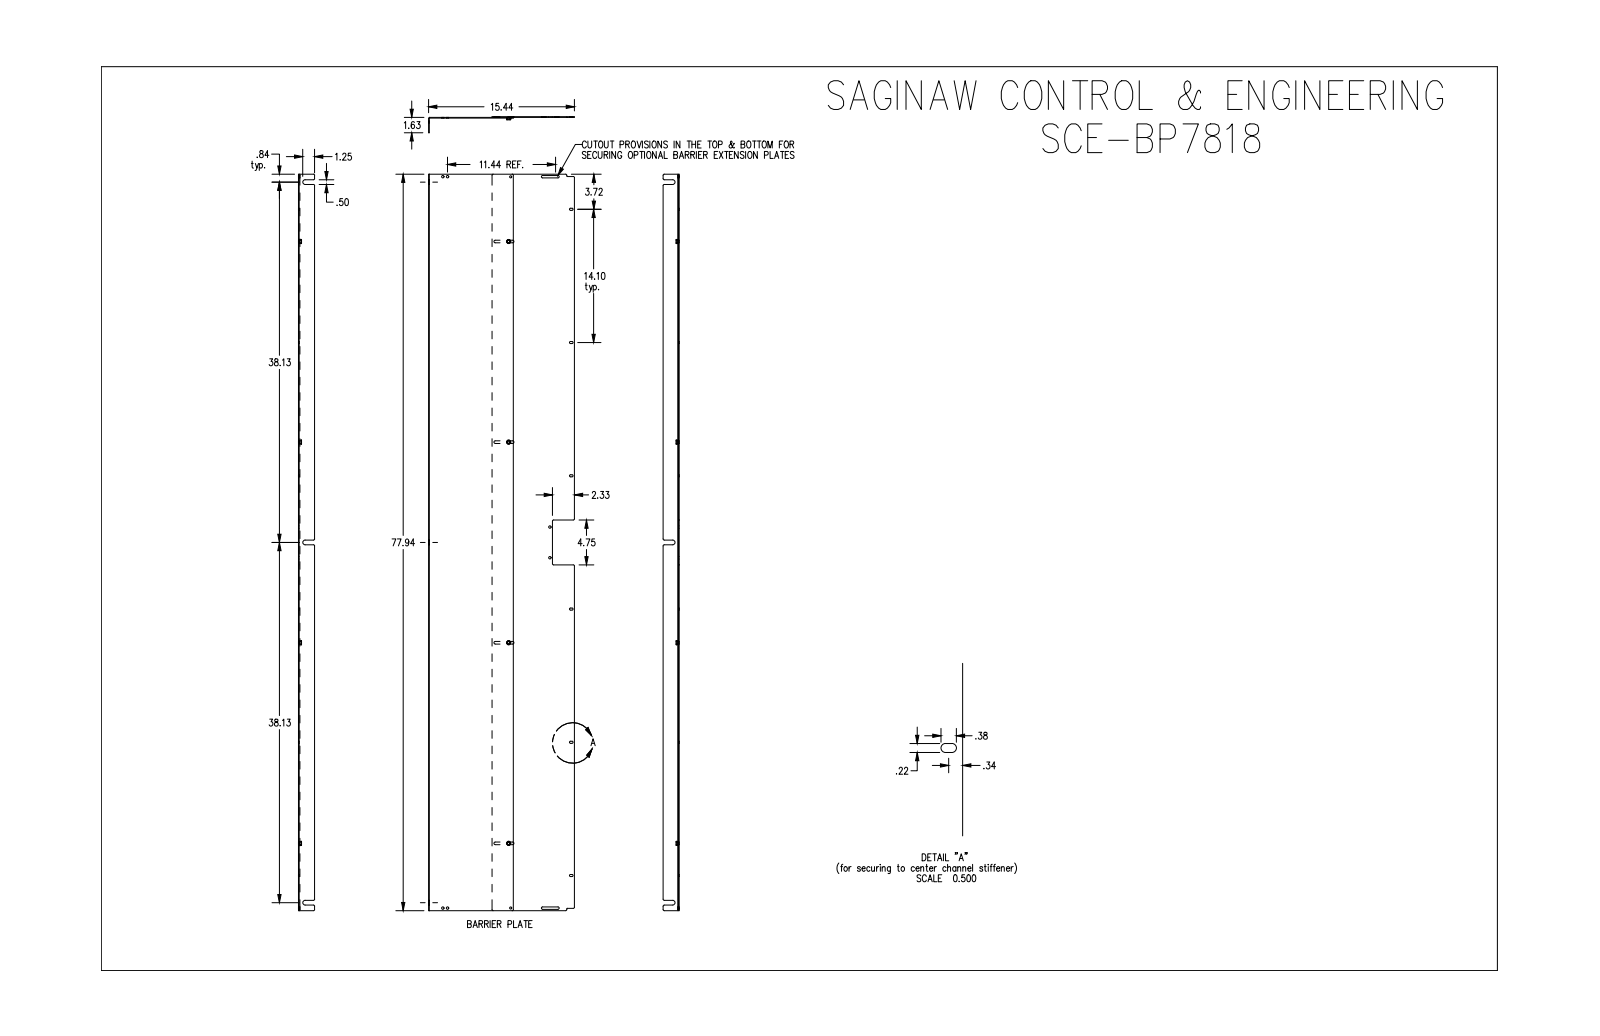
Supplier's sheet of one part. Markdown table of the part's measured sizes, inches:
| quantity | value |
| --- | --- |
| part name | SCE-BP7818 |
| STEP written by | SolidWorks 2019 (CONFIG_CONTROL_DESIGN) |
| units | inches |
| bodies | 6 solids, 154 faces (67 planar, 75 cylindrical, 12 other) |
| overall size | 77.938 × 15.44 × 1.7 |
| volume | 111 in³ |
| surface area | 2 991 in² |
| round holes (diameter × count) | 0.25 × 10, 0.344 × 4, 0.218 × 2 |
| round bosses / shafts (diameter × count) | 0.44 × 4, 0.343 × 4 |
| partial cylindrical surfaces (radius × count) | 0.125 × 24, 0.109 × 12, 0.141 × 8, 0.25 × 3, 0.063 × 2, 0.042 × 1, 0.117 × 1 |
| main face-to-face distances | 0.075, 0.15, 6.72, 6.645, 8.97, 8.895, 2.25, 1.7, 1.625, 1.55 |
| hole center spacings | 21.229, 0.5, 6.689, 6.847, 7.189, 9.426, 9.776, 9.996 |
